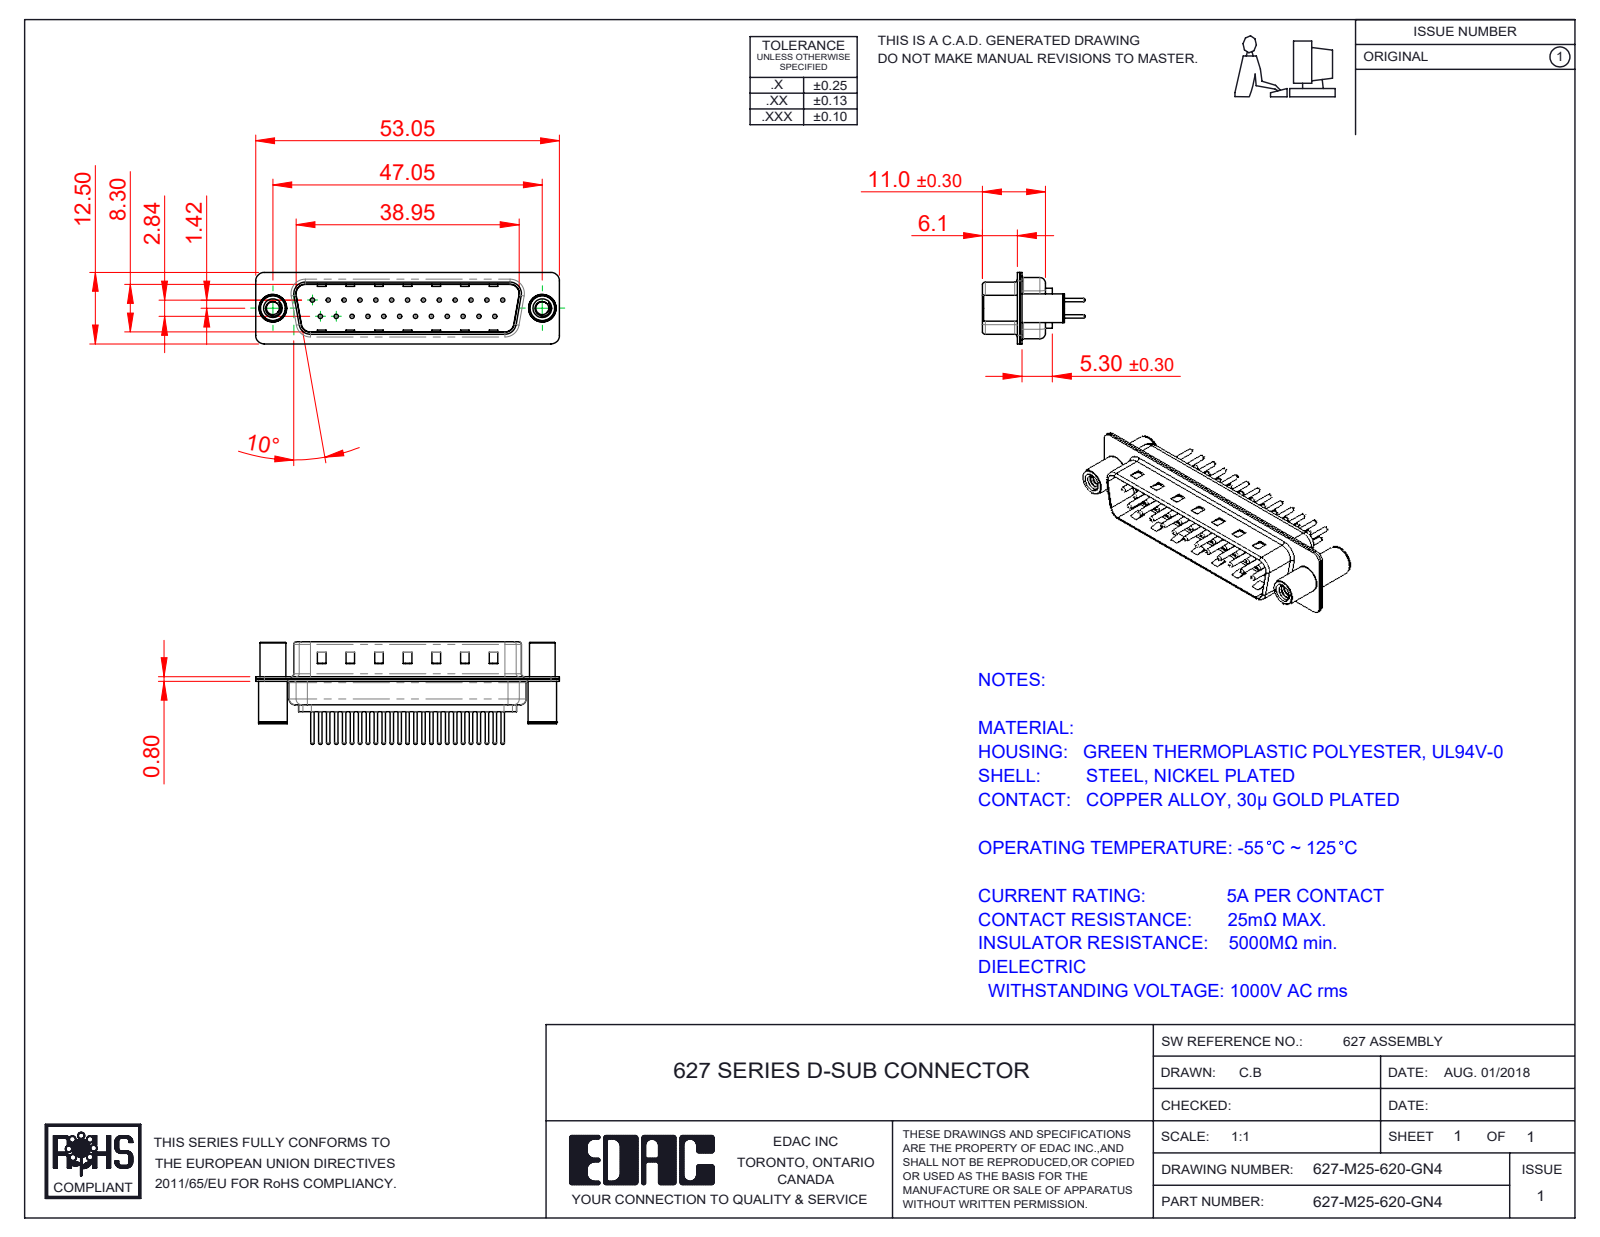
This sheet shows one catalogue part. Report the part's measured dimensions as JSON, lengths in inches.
{"part_name": "627M 4-40 Threaded Standoff and Board Spacer; 627-M25-620-GN4; 627M Housing_25 Contacts; 627M Shell Front_25 Contacts (+3 more)", "step_written_by": "SolidWorks 2020 (CONFIG_CONTROL_DESIGN)", "units": "inches", "bodies": {"solids": 30, "faces": 1387, "planar": 352, "cylindrical": 539, "other": 496}, "overall_size": [2.089, 0.705, 0.492], "volume_in3": 0.183, "surface_area_in2": 11.43, "round_holes": [[0.03, 25], [0.063, 25], [0.079, 25], [0.089, 2], [0.128, 2], [0.157, 2], [0.189, 2]], "round_bosses_or_shafts": [[0.059, 25], [0.024, 25], [0.197, 2], [0.193, 2], [0.177, 2]], "partial_cylinders_radius": [[0.059, 16], [0.079, 12], [0.02, 8], [0.063, 8], [0.01, 4], [0.024, 4], [0.026, 4], [0.035, 4]], "face_to_face_distances": [0.016, 0.031, 0.374, 0.358, 0.343, 0.39, 0.047, 0.224, 0.24, 0.03], "hole_center_spacings": [0.124, 0.109, 0.218, 0.327, 0.436, 0.545, 0.654, 0.198]}
